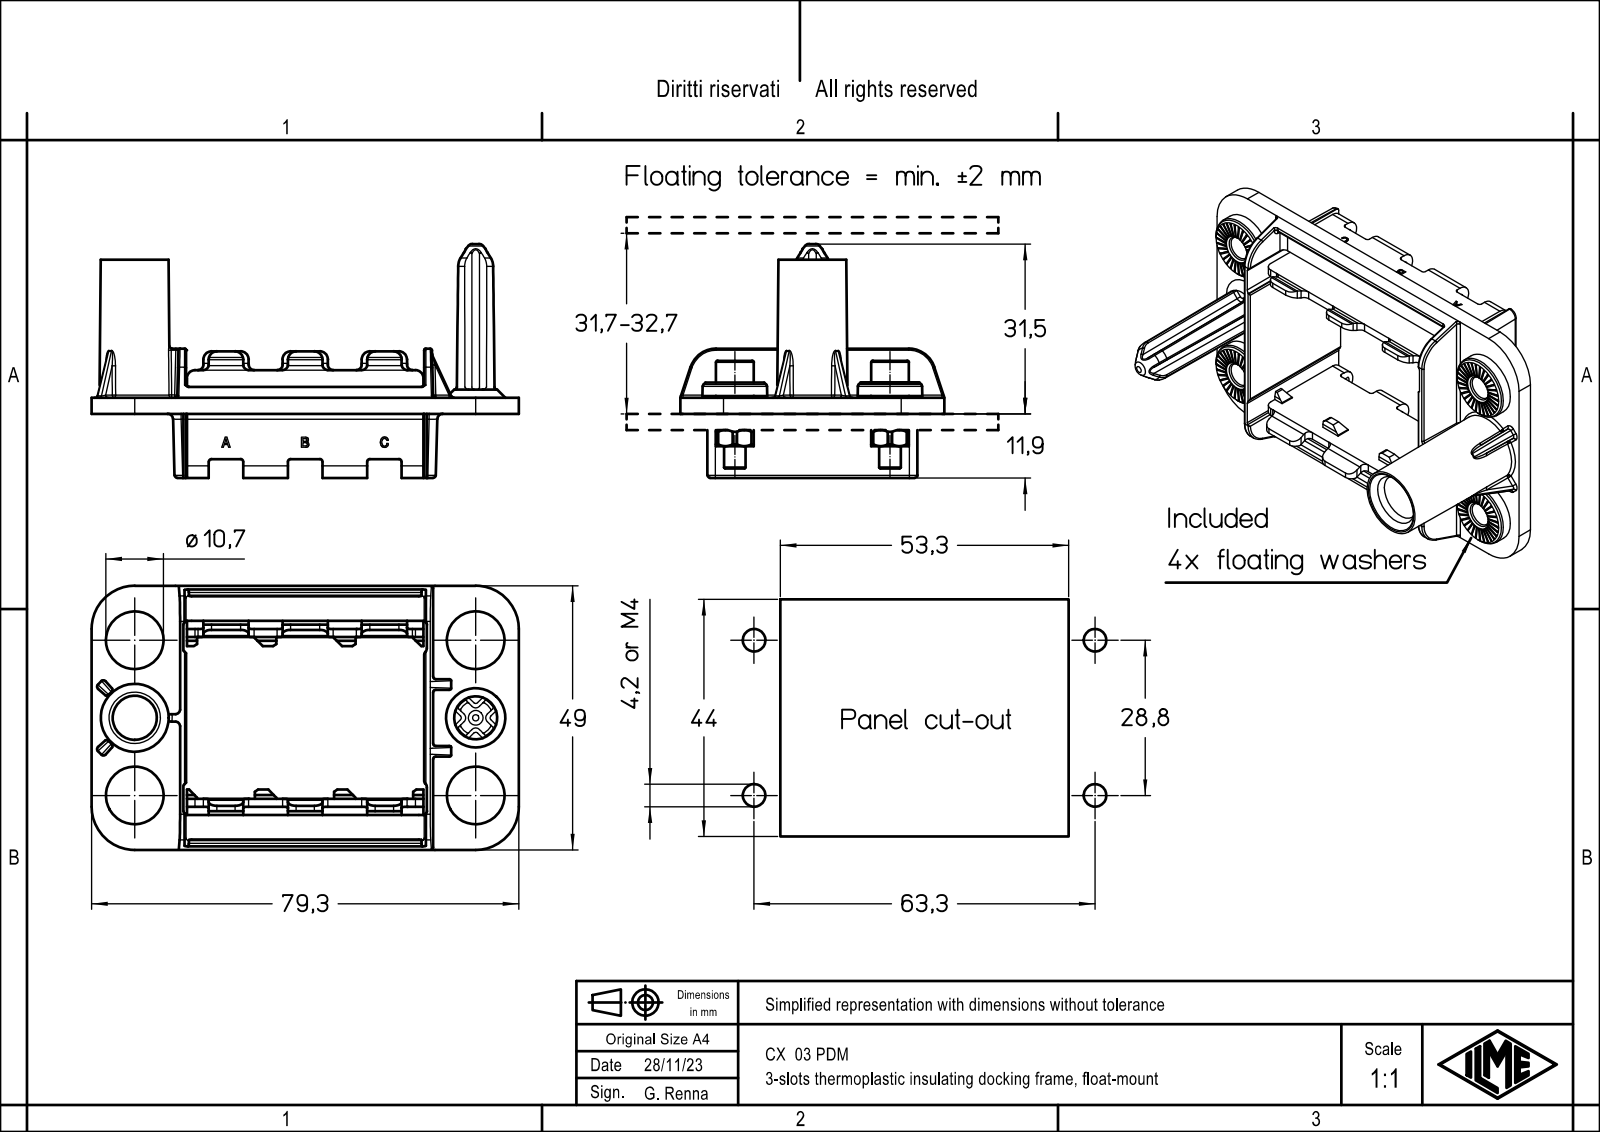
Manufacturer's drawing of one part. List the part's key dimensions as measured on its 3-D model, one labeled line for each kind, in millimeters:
Part name (STEP PRODUCT): CX 03 PDM
STEP written by: Creo Elements/Direct Modeling 20.1B 02-Apr-2019 (C) Parametric Technology GmbH (AUTOMOTIVE_DESIGN)
Units: millimetres
Bodies: 1 solid, 456 faces (267 planar, 129 cylindrical, 60 other)
Overall size (bounding box): 79.3 × 49 × 43.4
Volume: 16 771 mm³ · Surface area: 19 031 mm²
Round holes (diameter × count): ⌀10.7 ×4
Partial cylindrical surfaces — rounded edges, fillets, slot ends (radius × count): R1 ×18, R1.5 ×18, R0.1 ×15, R0.5 ×12, R8 ×4, R0.75 ×2, R2 ×2, R2.25 ×2
Main face-to-face distances: 1.5, 3, 34.5, 33, 31.5, 36, 4.5, 37.5, 0.5, 48.38
Hole centre spacings: 28.8, 63.3, 69.54
